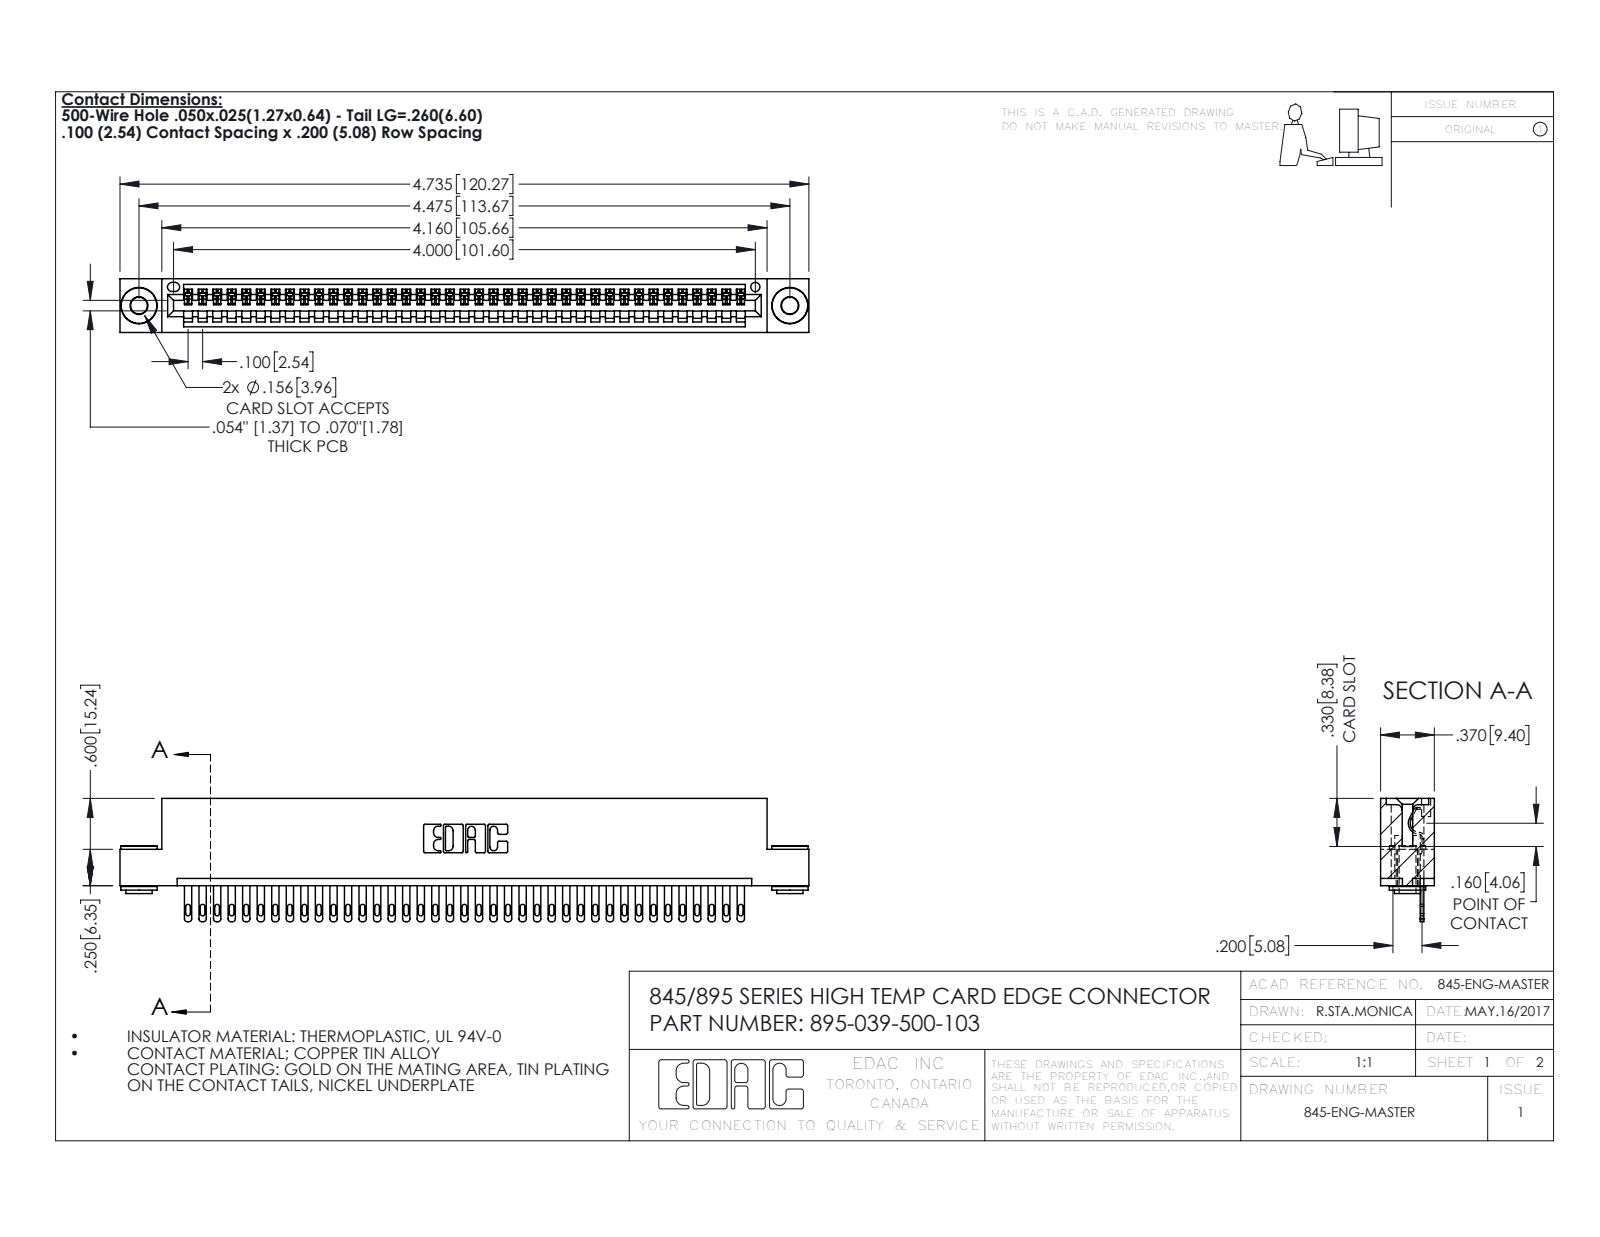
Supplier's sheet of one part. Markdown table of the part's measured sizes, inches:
| quantity | value |
| --- | --- |
| part name | 345-292-001_345-293-100; 845 Part_Flush Mounting Lugs - 0.156 Dia-TH; 345-250-002_345-250-002-102; 895-039-500-103 |
| STEP written by | SolidWorks 2020 (CONFIG_CONTROL_DESIGN) |
| units | inches |
| bodies | 42 solids, 2270 faces (1416 planar, 846 cylindrical, 8 other) |
| overall size | 4.735 × 0.847 × 0.37 |
| volume | 0.698 in³ |
| surface area | 23.97 in² |
| round holes (diameter × count) | 0.116 × 2, 0.156 × 2, 0.064 × 1 |
| round bosses / shafts (diameter × count) | 0.25 × 2, 0.18 × 2, 0.136 × 2 |
| partial cylindrical surfaces (radius × count) | 0.006 × 78, 0.016 × 78, 0.02 × 78, 0.01 × 22, 0.007 × 6, 0.031 × 6, 0.026 × 3, 0.031 × 2 |
| main face-to-face distances | 0.072, 0.298, 0.37, 0.2, 0.025, 0.098, 0.272, 0.225, 0.149, 0.072 |
| hole center spacings | 0.27, 4.239, 4.475 |
